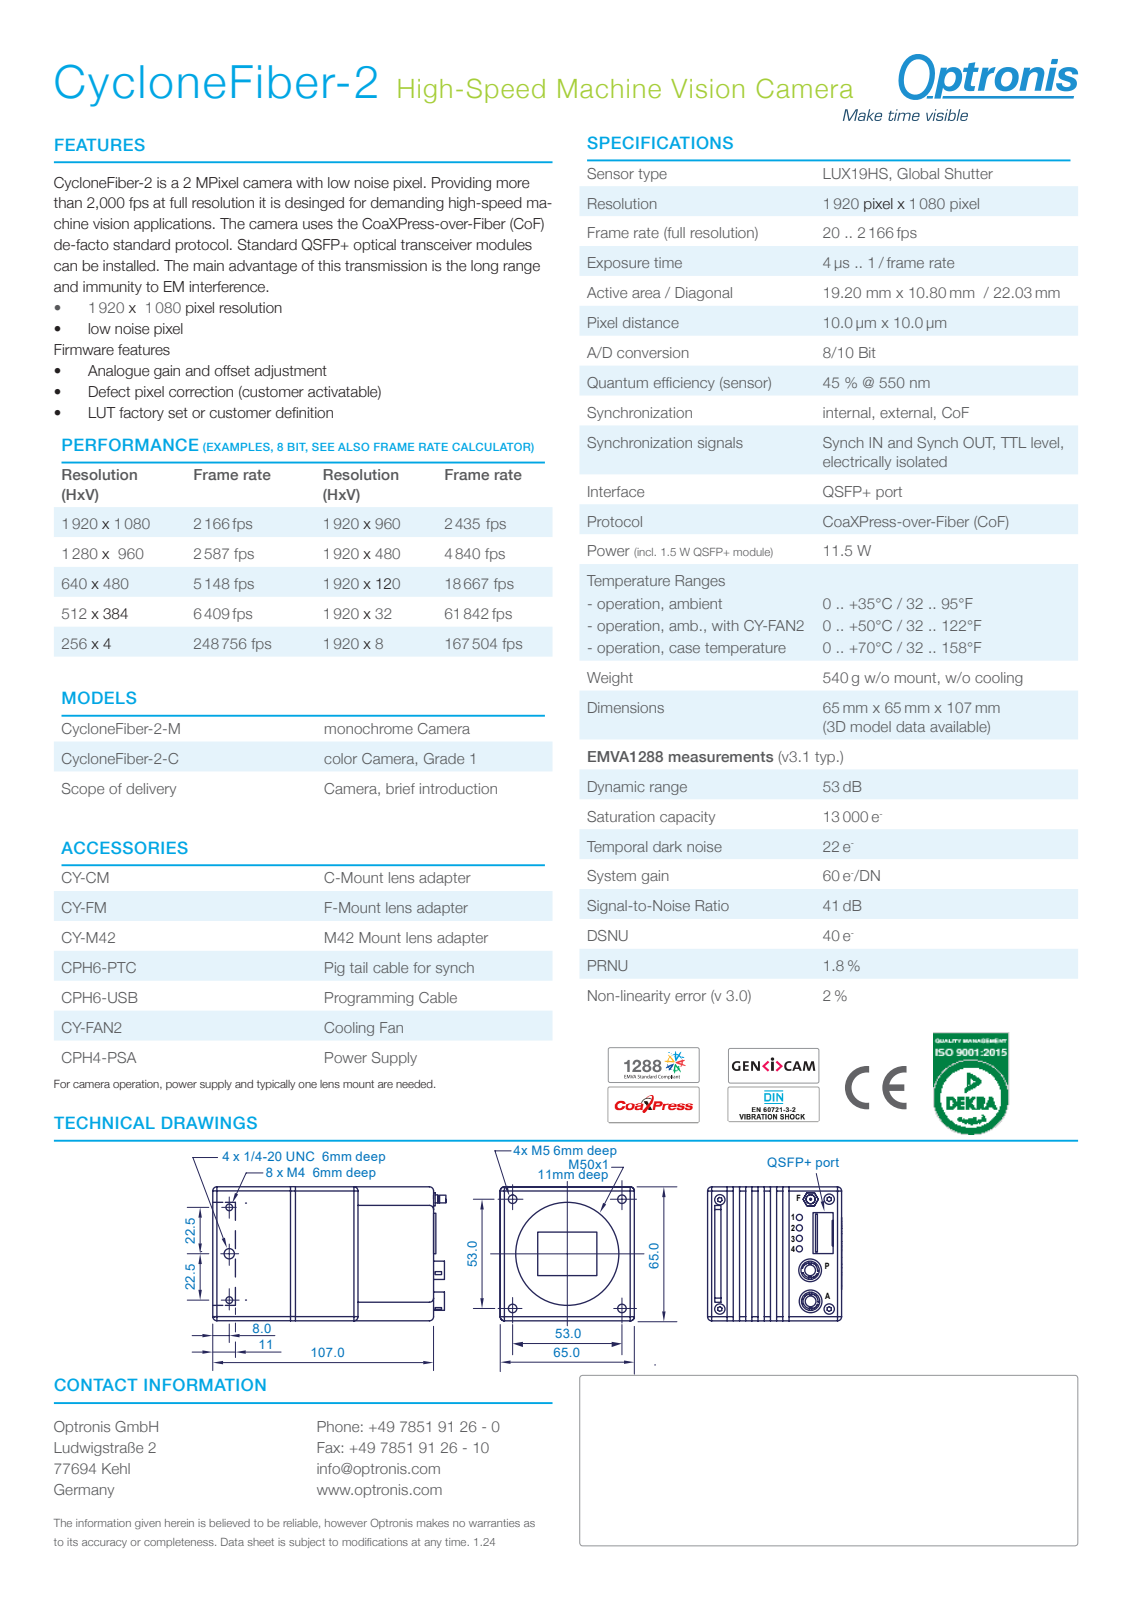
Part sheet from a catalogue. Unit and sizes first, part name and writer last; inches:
Units: inches
Overall size (bounding box): 4.232 × 2.559 × 2.559
Round holes (diameter × count): ⌀0.039 ×28, ⌀0.031 ×16, ⌀0.106 ×12, ⌀0.02 ×10, ⌀0.062 ×8, ⌀0.079 ×4, ⌀0.087 ×4, ⌀0.112 ×4, ⌀0.128 ×4, ⌀0.165 ×4, ⌀0.197 ×4, ⌀0.217 ×4
Round bosses / shafts (diameter × count): ⌀0.034 ×345, ⌀0.012 ×345, ⌀0.043 ×12, ⌀0.098 ×8, ⌀0.185 ×4, ⌀0.177 ×4, ⌀0.15 ×4, ⌀0.138 ×4
Partial cylindrical surfaces — rounded edges, fillets, slot ends (radius × count): R0.01 ×188, R0.008 ×60, R0.004 ×45, R0.02 ×44, R0.039 ×40, R0.079 ×34, R0.005 ×28, R0.118 ×28
Main face-to-face distances: 0.118, 0.236, 0.354, 0.472, 0.591, 0.709, 0.827, 0.945, 0.079, 1.063
Hole centre spacings: 0.132, 0.308, 0.265, 0.197, 0.5, 0.283, 0.432, 0.177
Volume: 8.198 in³ · Surface area: 177.3 in²
Bodies: 5 solids, 5550 faces (2900 planar, 2384 cylindrical, 266 other)
Part name (STEP PRODUCT): 1200-MG-13_CycloneFiber_short
STEP written by: Autodesk Inventor 2026 (AUTOMOTIVE_DESIGN)
